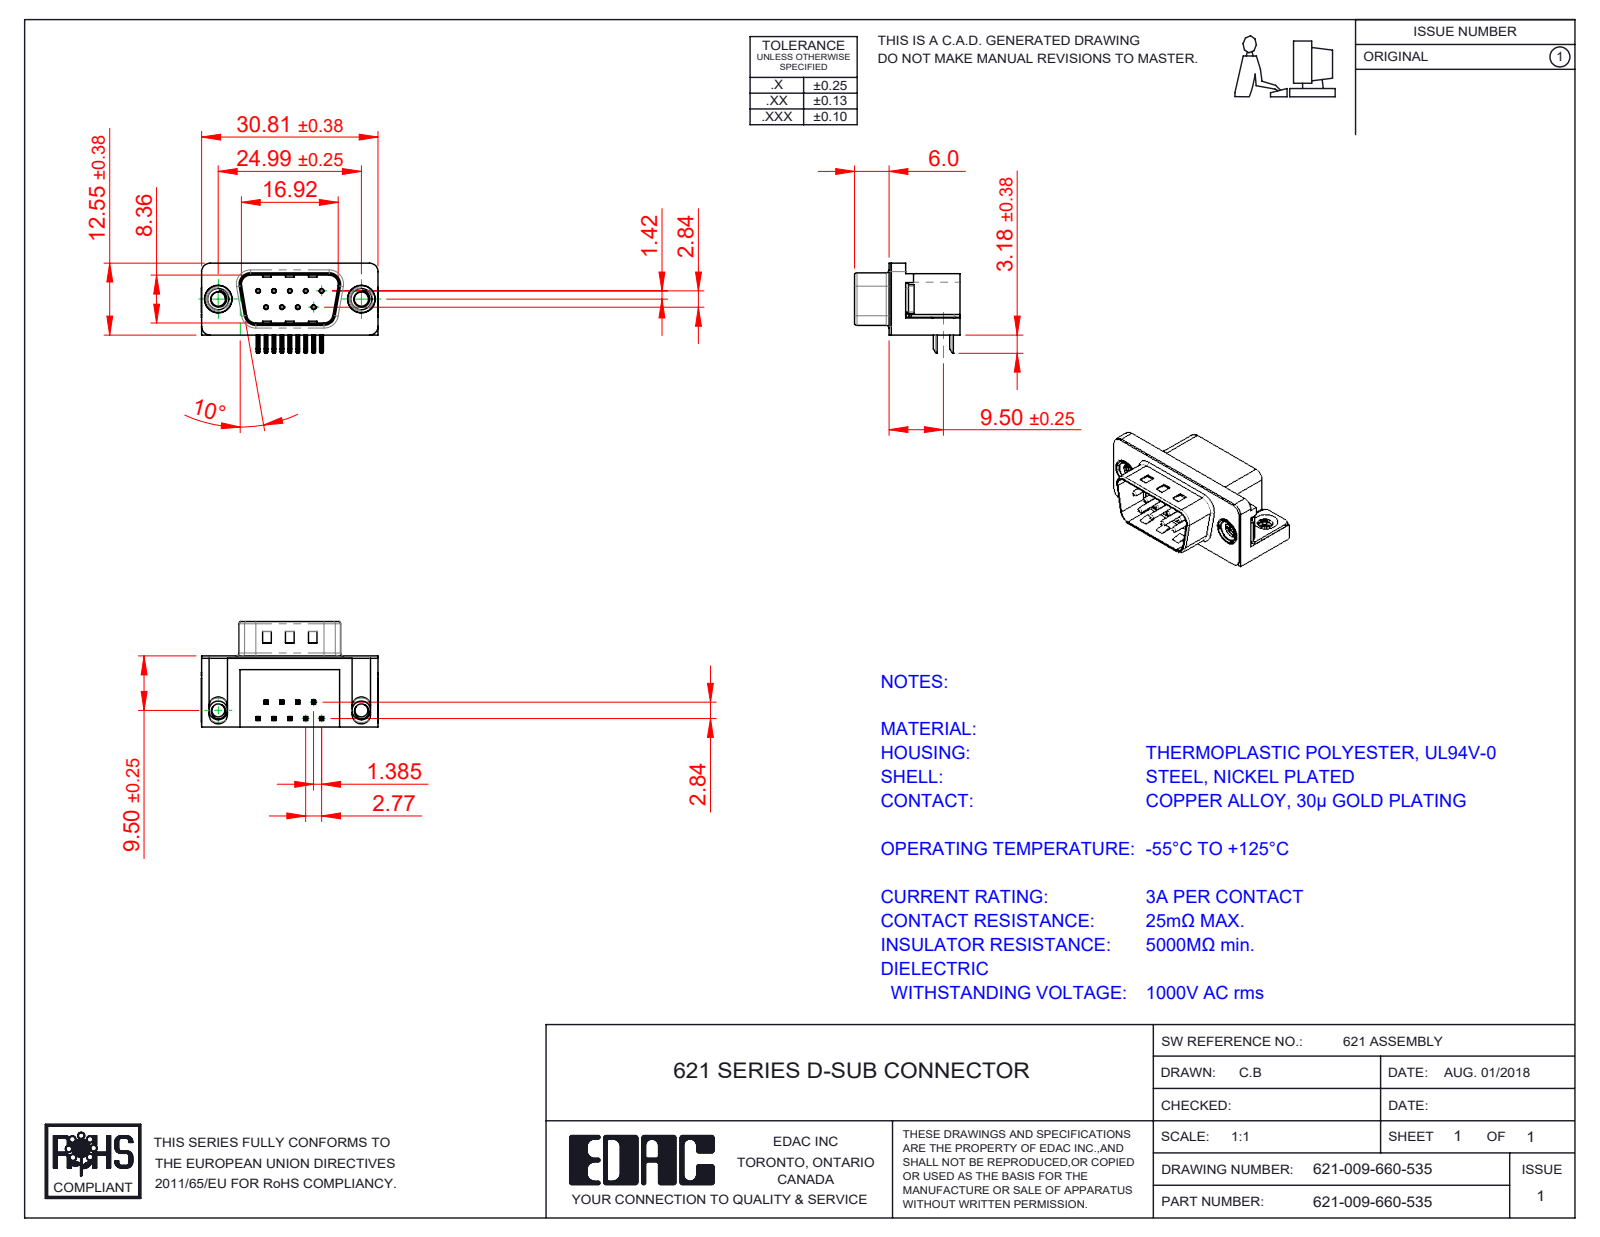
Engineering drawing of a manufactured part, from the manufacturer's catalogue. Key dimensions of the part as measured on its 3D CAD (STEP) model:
Part name (STEP PRODUCT): 621 2 Prong Board Lock; 621-009-660-535; 621 M3 Threaded Rivet; 621 Contact Top (+3 more)
STEP written by: SolidWorks 2016 (CONFIG_CONTROL_DESIGN)
Units: millimetres
Bodies: 15 solids, 1031 faces (605 planar, 327 cylindrical, 99 other)
Overall size (bounding box): 30.89 × 18.4 × 16.25
Volume: 3 240 mm³ · Surface area: 4 430 mm²
Round holes (diameter × count): ⌀0.35 ×9, ⌀0.8 ×9, ⌀2.5 ×2, ⌀4 ×2, ⌀4.8 ×2, ⌀5 ×2
Round bosses / shafts (diameter × count): ⌀0.75 ×9, ⌀4.9 ×2, ⌀4.75 ×2, ⌀3.9 ×2
Partial cylindrical surfaces — rounded edges, fillets, slot ends (radius × count): R0.25 ×44, R0.12 ×18, R1 ×16, R0.5 ×14, R1.5 ×8, R1.6 ×8, R0.32 ×4, R0.9 ×4
Main face-to-face distances: 0.4, 12, 12.4, 10.35, 0.5, 9.5, 2.5, 2.9, 2.1, 0.35
Hole centre spacings: 3.16, 2.77, 5.54, 5.03, 5.04, 8.31, 7.48, 7.49
